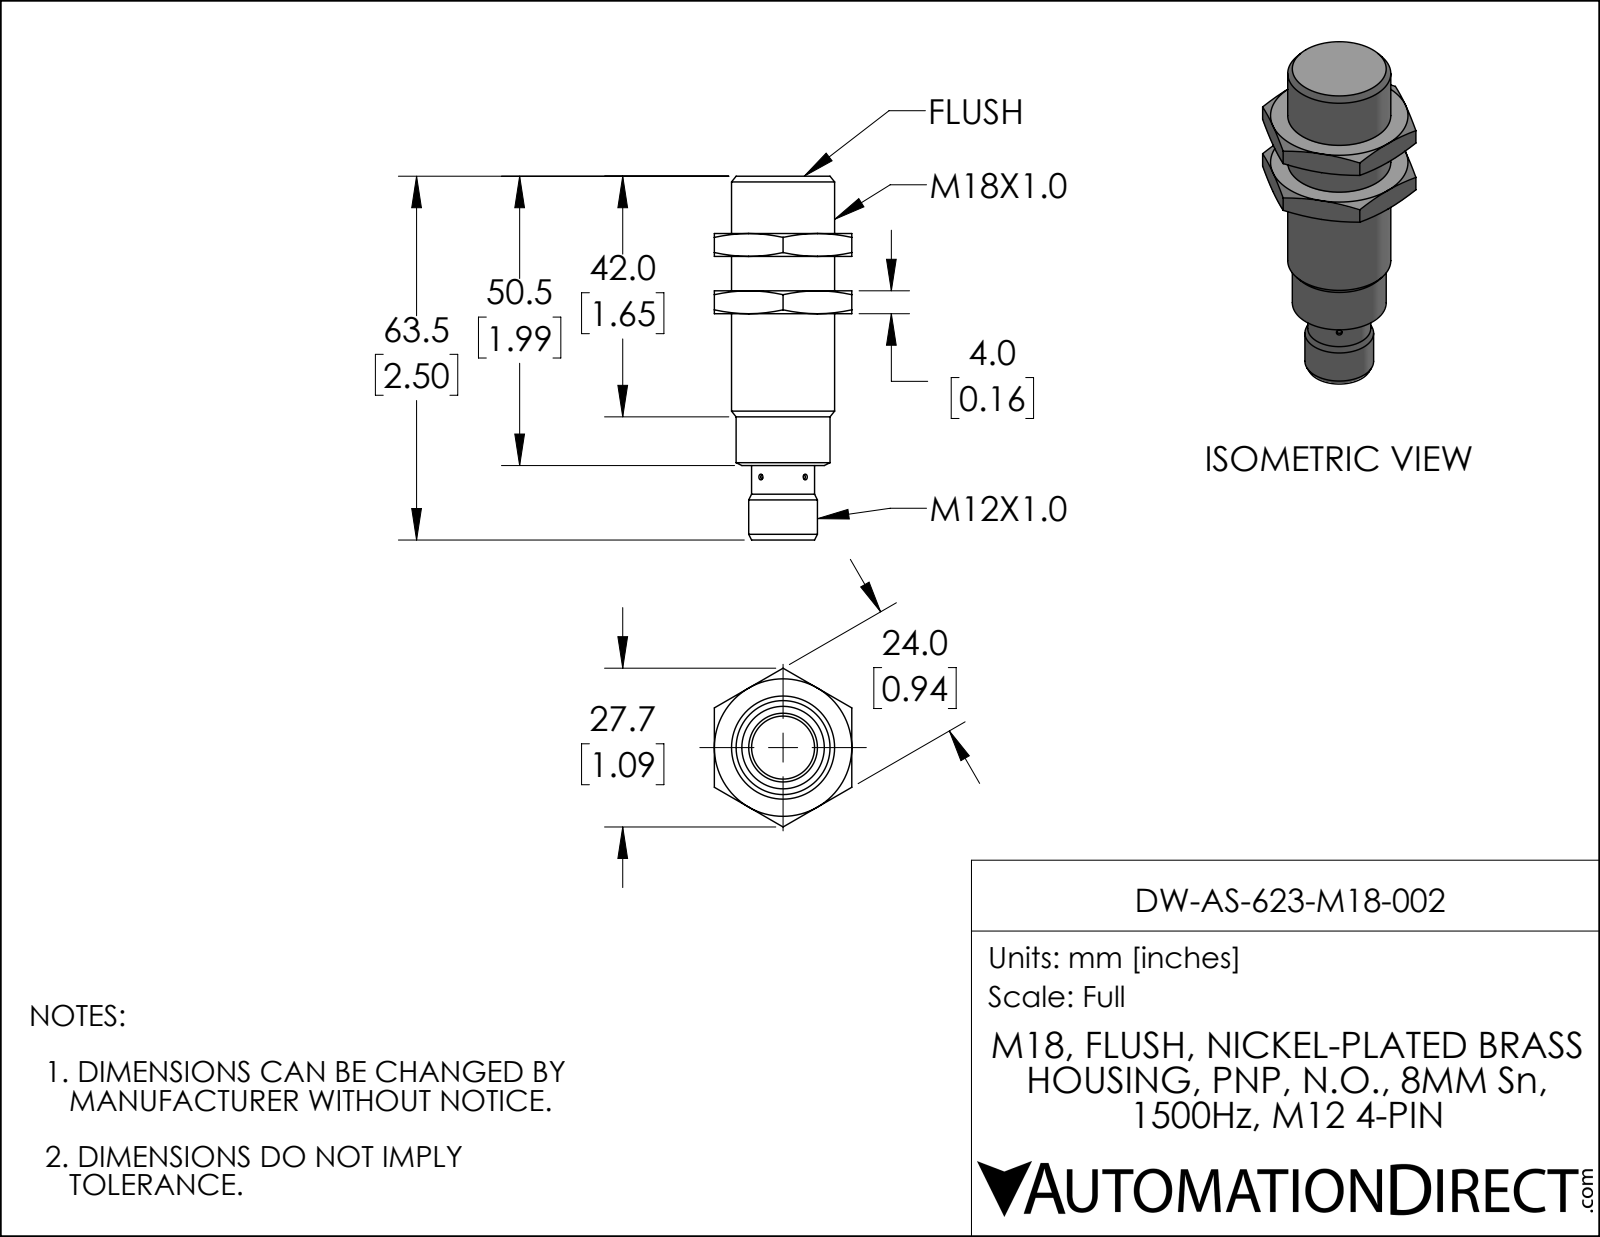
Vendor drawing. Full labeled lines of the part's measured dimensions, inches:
Part name (STEP PRODUCT): DW-AS-623-M18-002
STEP written by: SolidWorks 2019 (AUTOMOTIVE_DESIGN)
Units: inches
Bodies: 1 solid, 62 faces (23 planar, 10 cylindrical, 29 other)
Overall size (bounding box): 2.5 × 1.091 × 0.945
Volume: 0.958 in³ · Surface area: 7.52 in²
Round holes (diameter × count): ⌀0.039 ×2
Round bosses / shafts (diameter × count): ⌀0.709 ×1, ⌀0.646 ×1, ⌀0.472 ×1, ⌀0.433 ×1
Main face-to-face distances: 0.394, 0.945, 0.551, 0.157, 0.787, 0.236, 2.5, 2.106, 1.949, 1.713
